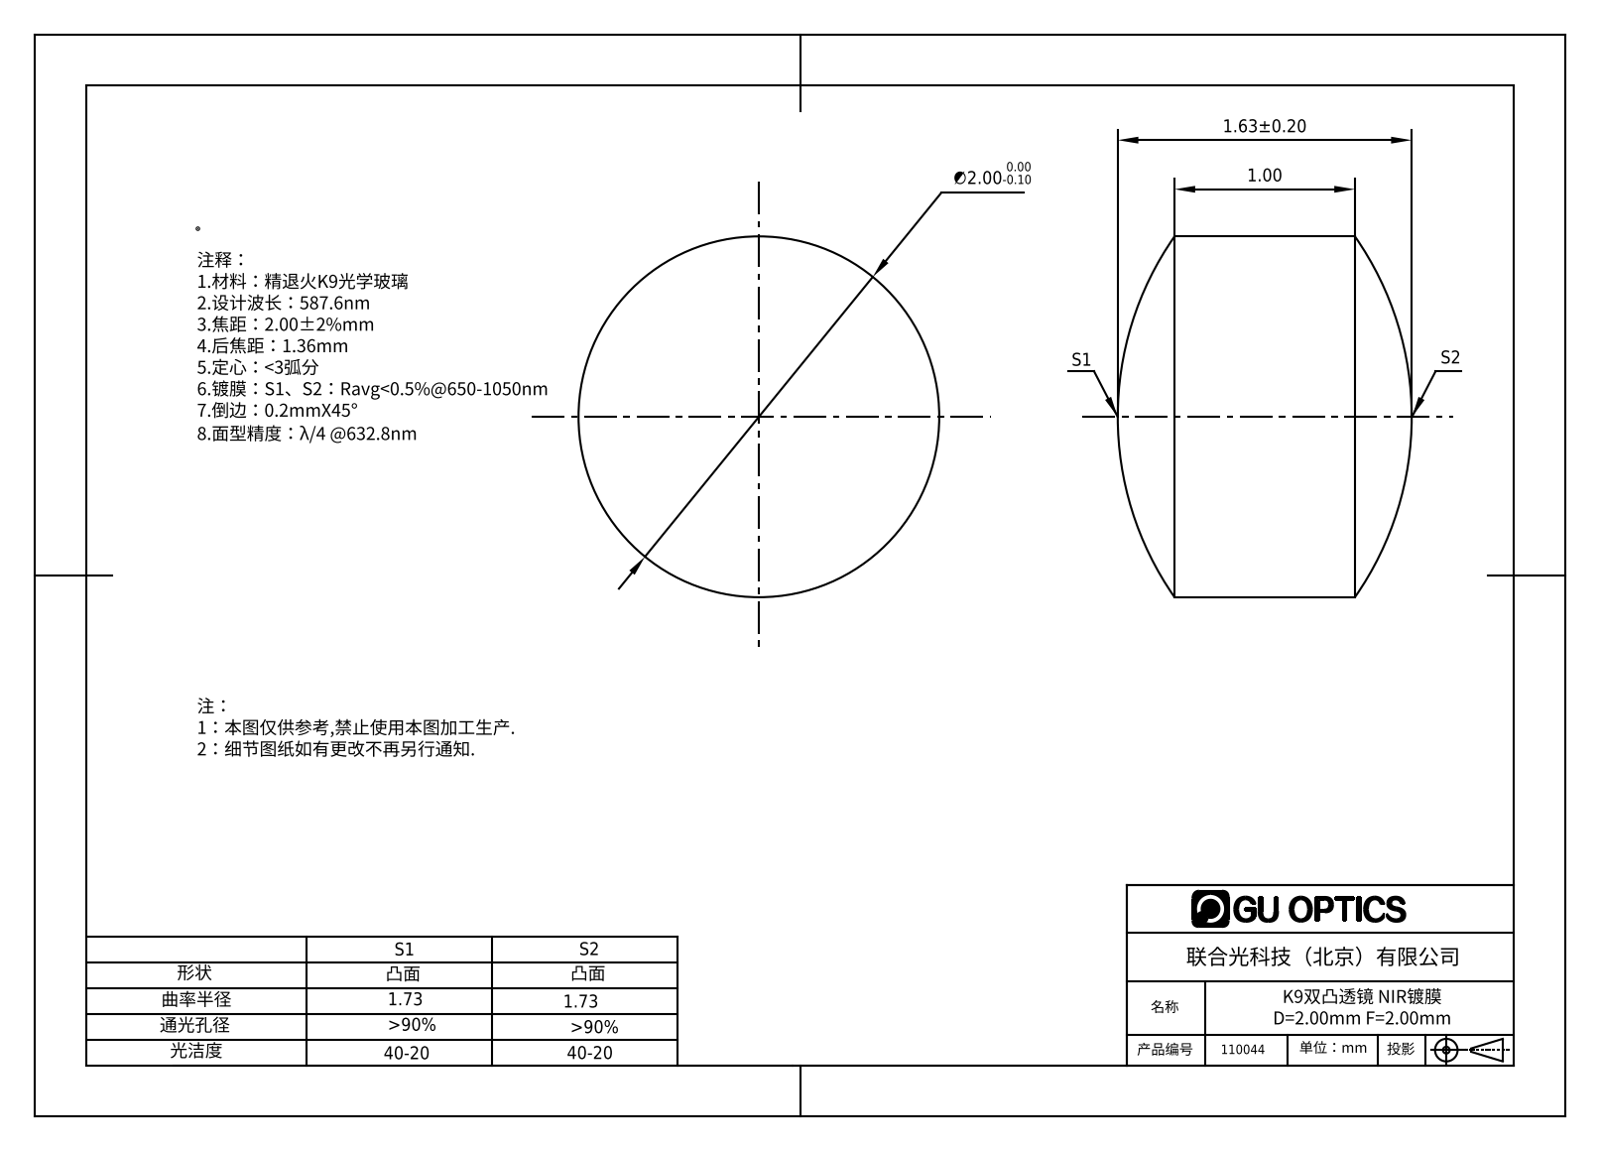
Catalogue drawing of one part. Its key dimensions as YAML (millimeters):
part_name: "110000"
step_written_by: "SolidWorks 2016 (CONFIG_CONTROL_DESIGN)"
units: millimeters
bodies: {solids: 1, faces: 6, planar: 0, cylindrical: 2, other: 4}
overall_size: [2, 2, 1.63]
volume: 4
surface_area: 13
round_bosses_or_shafts:
  - {diameter: 2, count: 1}
